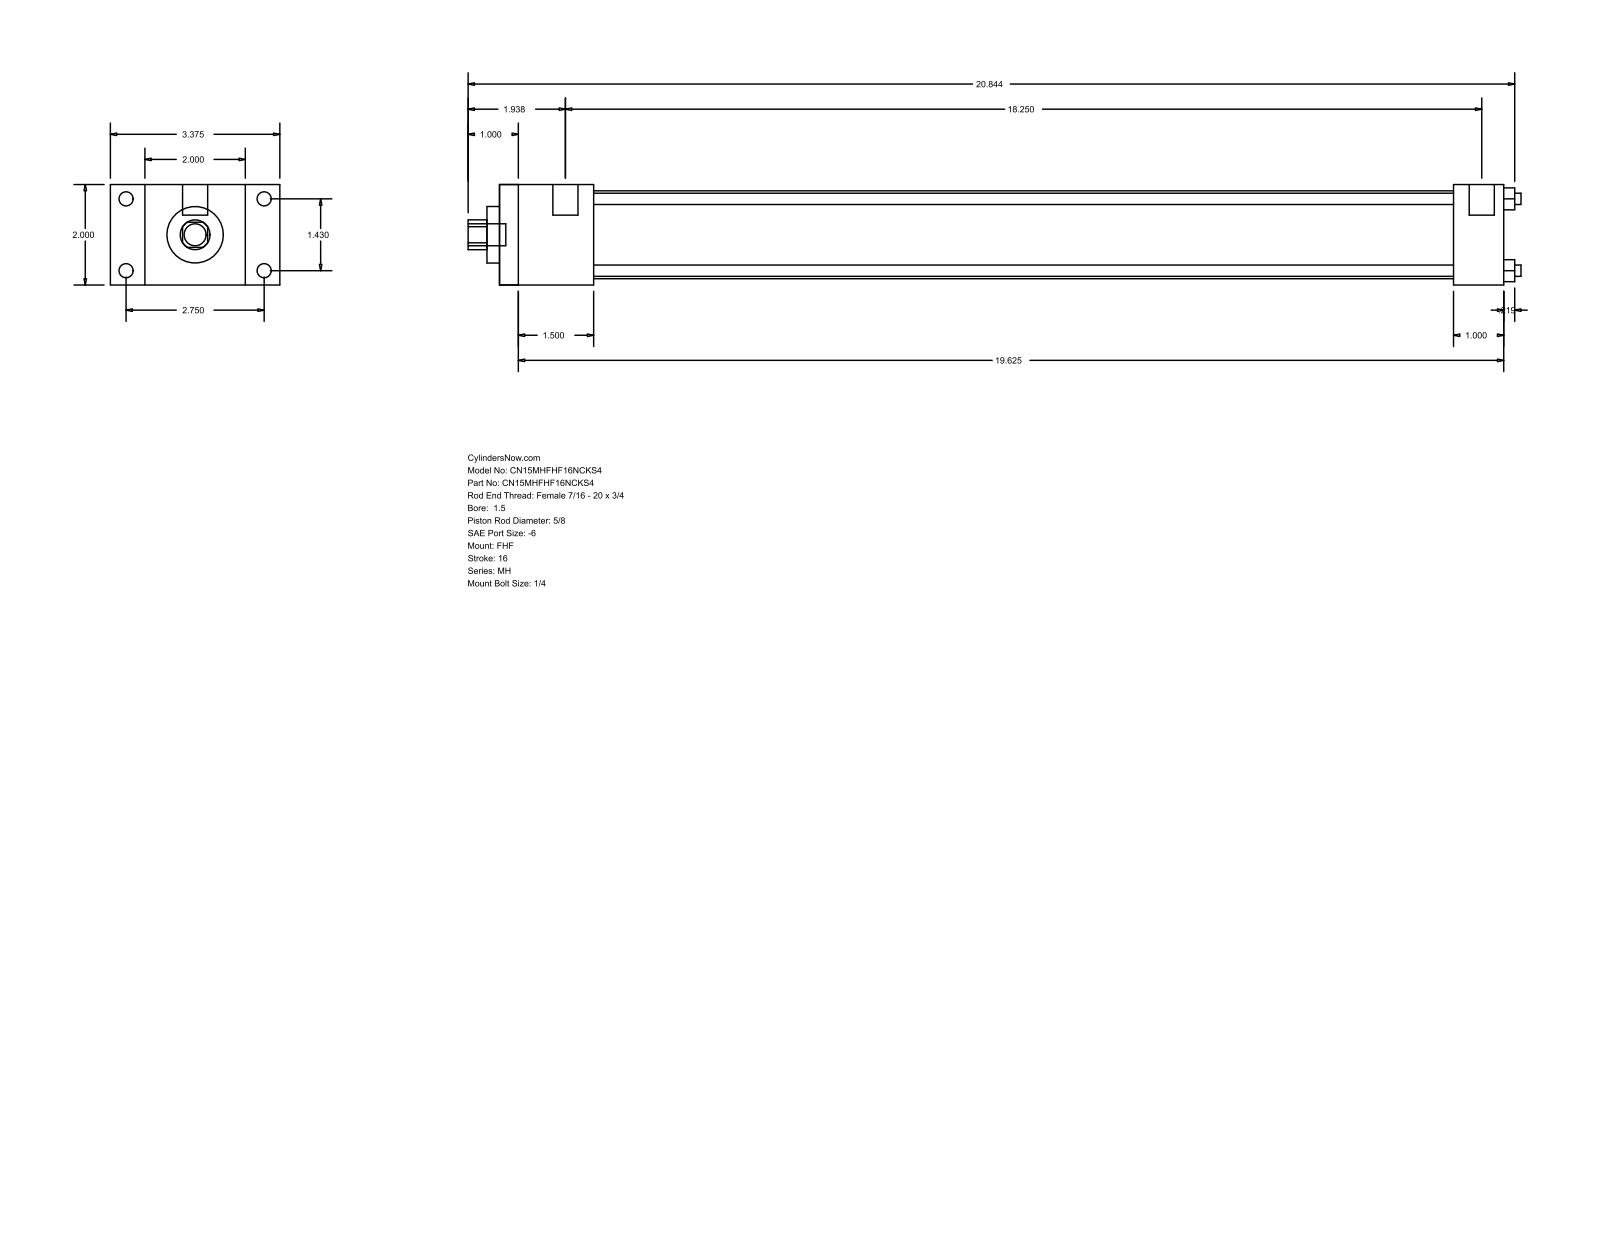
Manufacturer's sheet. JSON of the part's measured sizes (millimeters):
{"part_name": "MH_FHF__0150_0.625", "step_written_by": "GSSL Pune (CONFIG_CONTROL_DESIGN)", "units": "millimeters", "bodies": {"solids": 0, "faces": 88, "planar": 60, "cylindrical": 28, "other": 0}, "overall_size": [532.61, 85.72, 50.8], "round_holes": [[5.71, 4], [15.88, 1], [28.57, 1], [44.45, 1]], "round_bosses_or_shafts": [[7.14, 4], [5.56, 4], [12.7, 2], [11.11, 1]], "partial_cylinders_radius": [[7.54, 1]], "face_to_face_distances": [50.8, 17.46, 68.26, 47.62, 85.72, 508, 460.38, 482.6, 434.98, 25.4], "hole_center_spacings": [25.68, 36.32, 51.36]}
